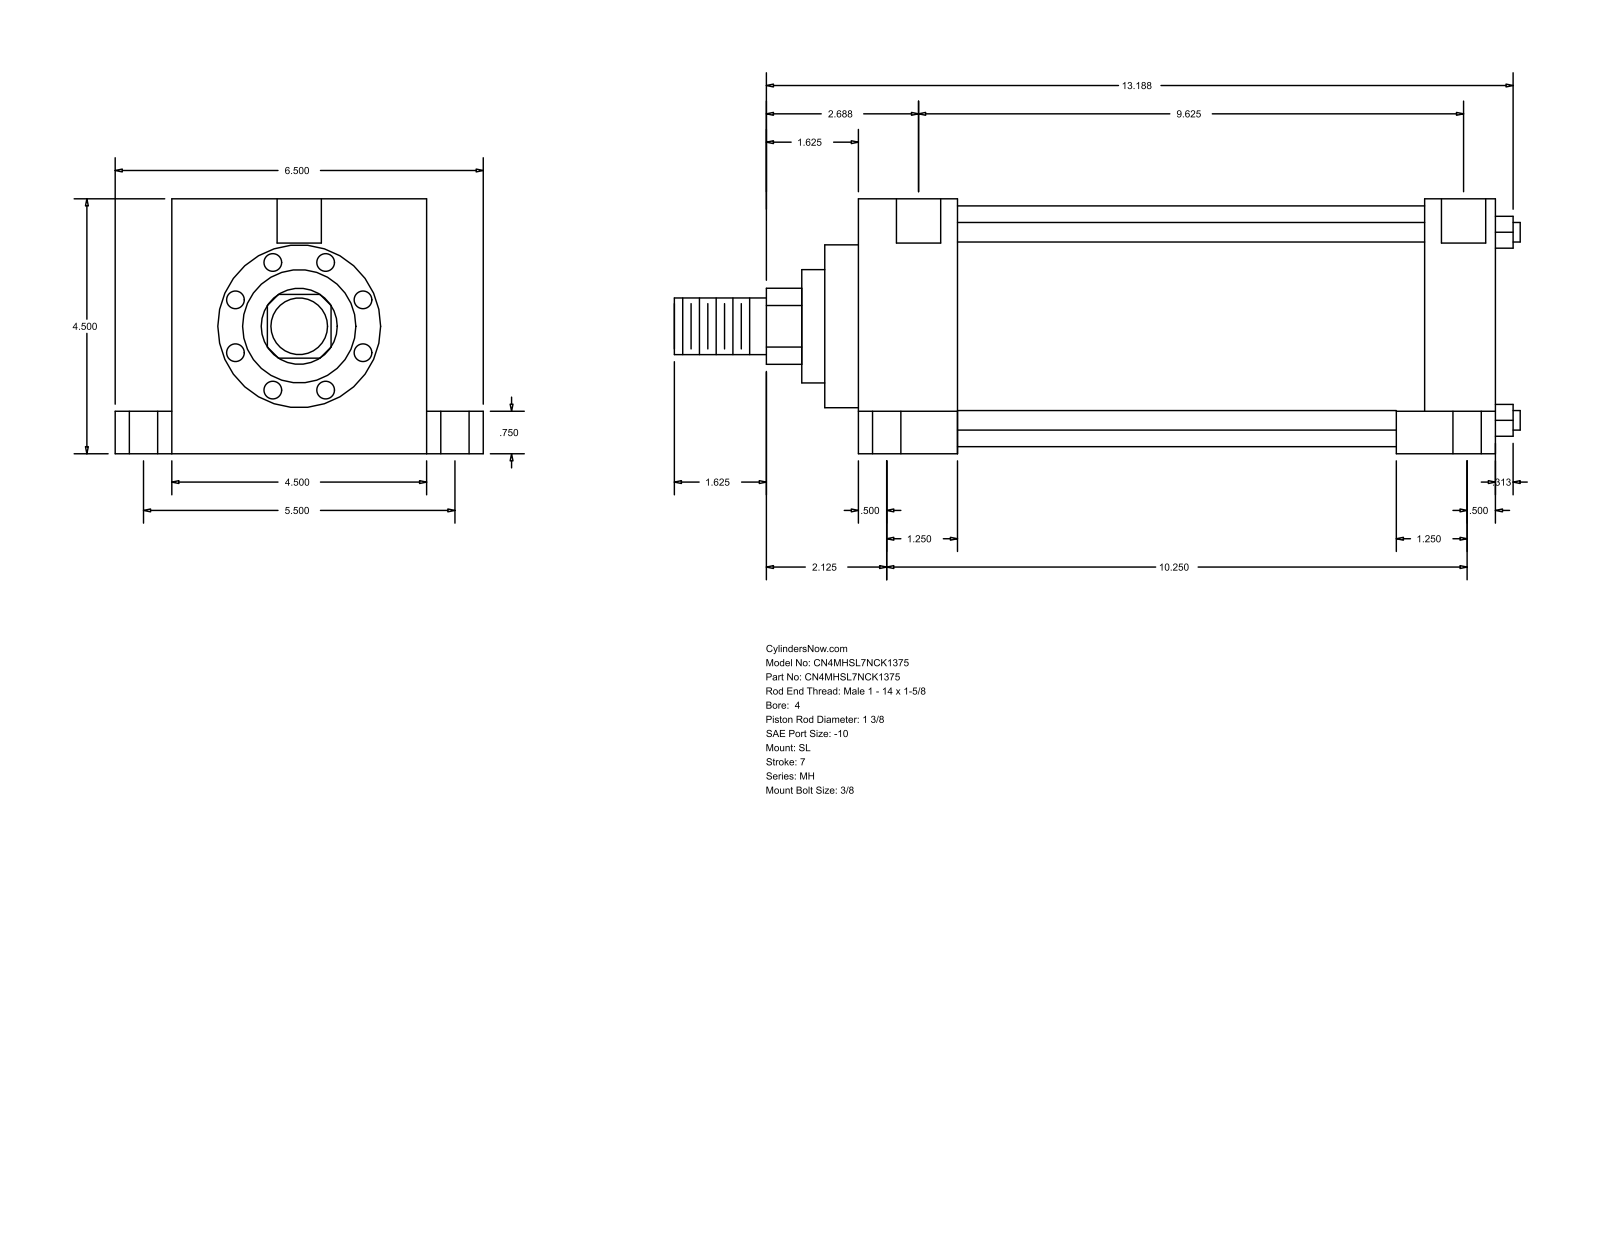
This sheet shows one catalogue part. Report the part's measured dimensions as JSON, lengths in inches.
{"part_name": "MH_SL__0400_1.375", "step_written_by": "GSSL Pune (CONFIG_CONTROL_DESIGN)", "units": "inches", "bodies": {"solids": 0, "faces": 110, "planar": 77, "cylindrical": 33, "other": 0}, "overall_size": [14.937, 6.5, 4.5], "round_holes": [[0.344, 4], [0.5, 4], [0.75, 4], [0.781, 2]], "round_bosses_or_shafts": [[0.345, 4], [4.25, 1], [2.875, 1], [2, 1], [1.375, 1], [1, 1]], "partial_cylinders_radius": [[0.672, 1]], "face_to_face_distances": [4.5, 11.25, 1.75, 9.5, 10, 8.25, 1.25, 1, 5.5, 0.75], "hole_center_spacings": [2.75, 2.751, 2.795, 2.807, 5.5, 9.75, 10.07, 10.13]}
